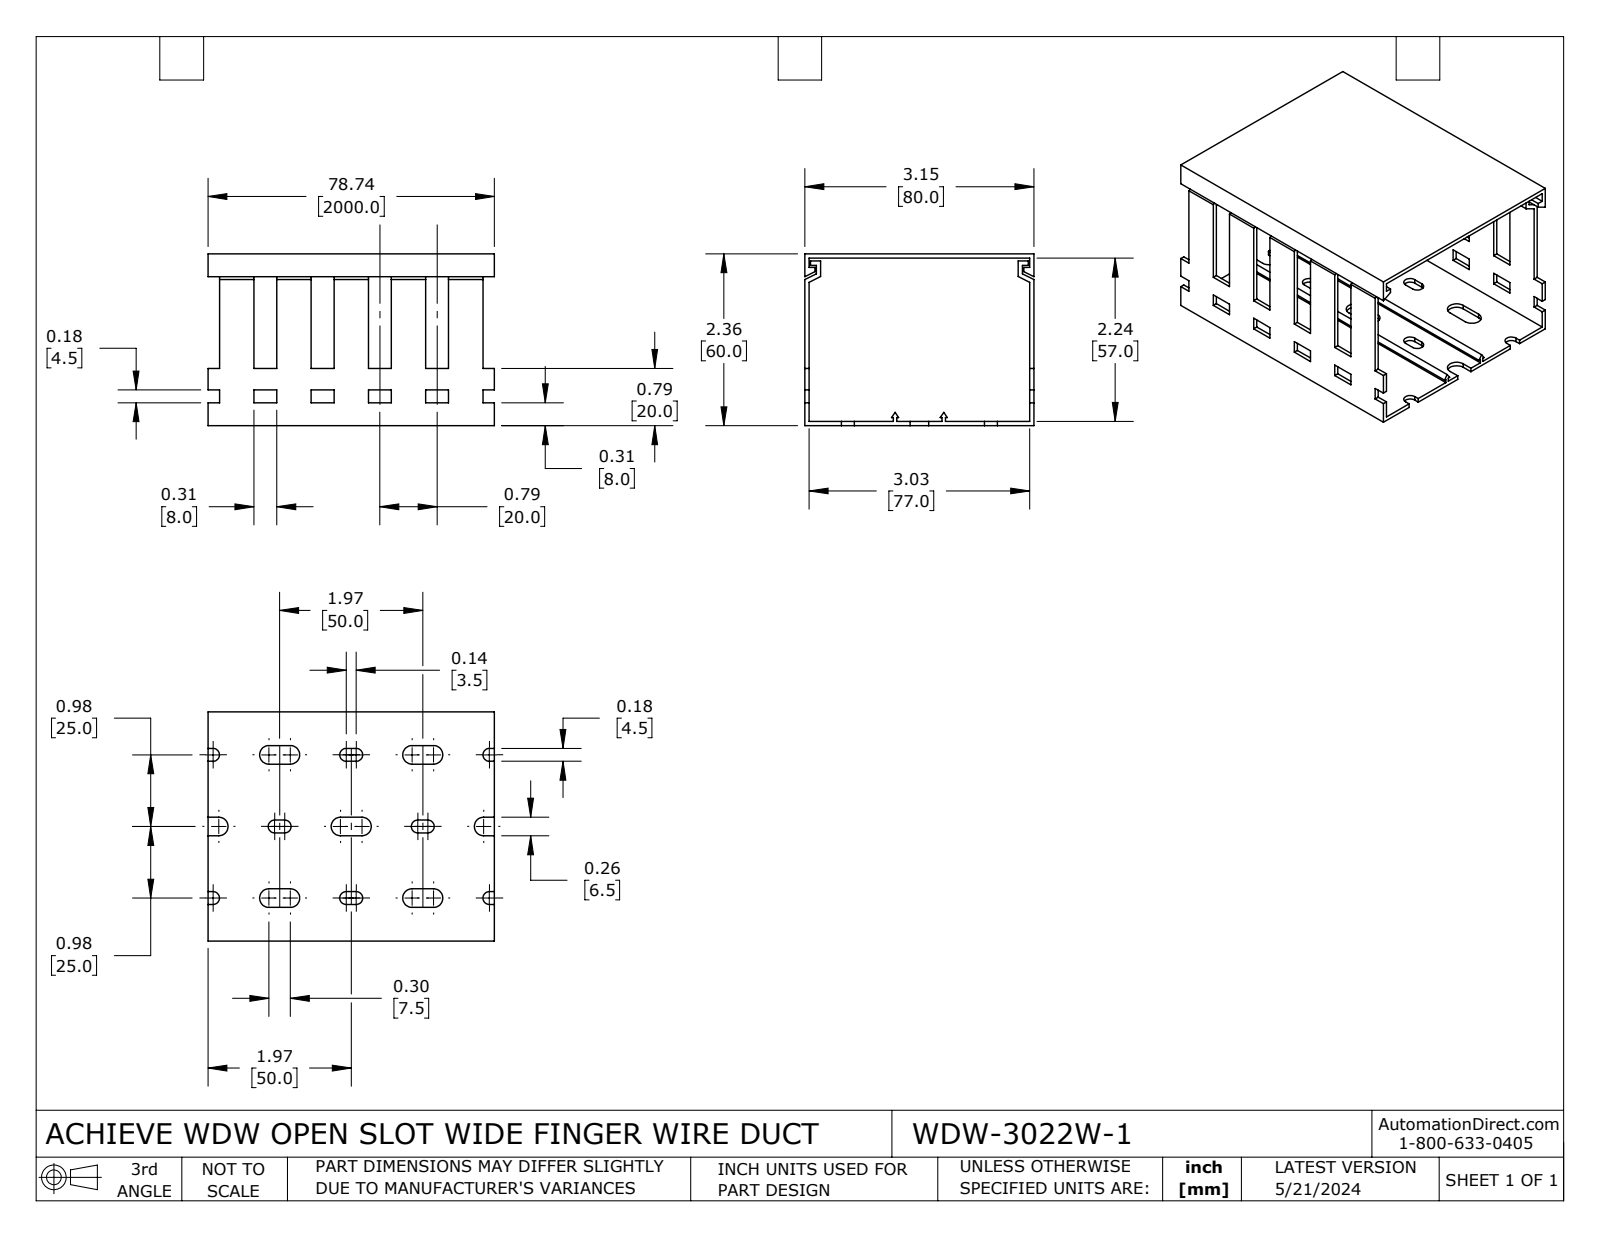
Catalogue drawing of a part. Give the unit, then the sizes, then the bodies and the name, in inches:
Units: inches
Overall size (bounding box): 3.937 × 3.15 × 2.362
Partial cylindrical surfaces — rounded edges, fillets, slot ends (radius × count): R0.089 ×12, R0.128 ×12
Main face-to-face distances: 0.059, 2.303, 2.362, 3.091, 2.244, 3.15, 3.031, 0.157, 0.787, 2.933
Volume: 2.377 in³ · Surface area: 85.69 in²
Bodies: 2 solids, 258 faces (222 planar, 36 cylindrical, 0 other)
Part name (STEP PRODUCT): WDW-3022W-1
STEP written by: SolidWorks 2023 (CONFIG_CONTROL_DESIGN)
